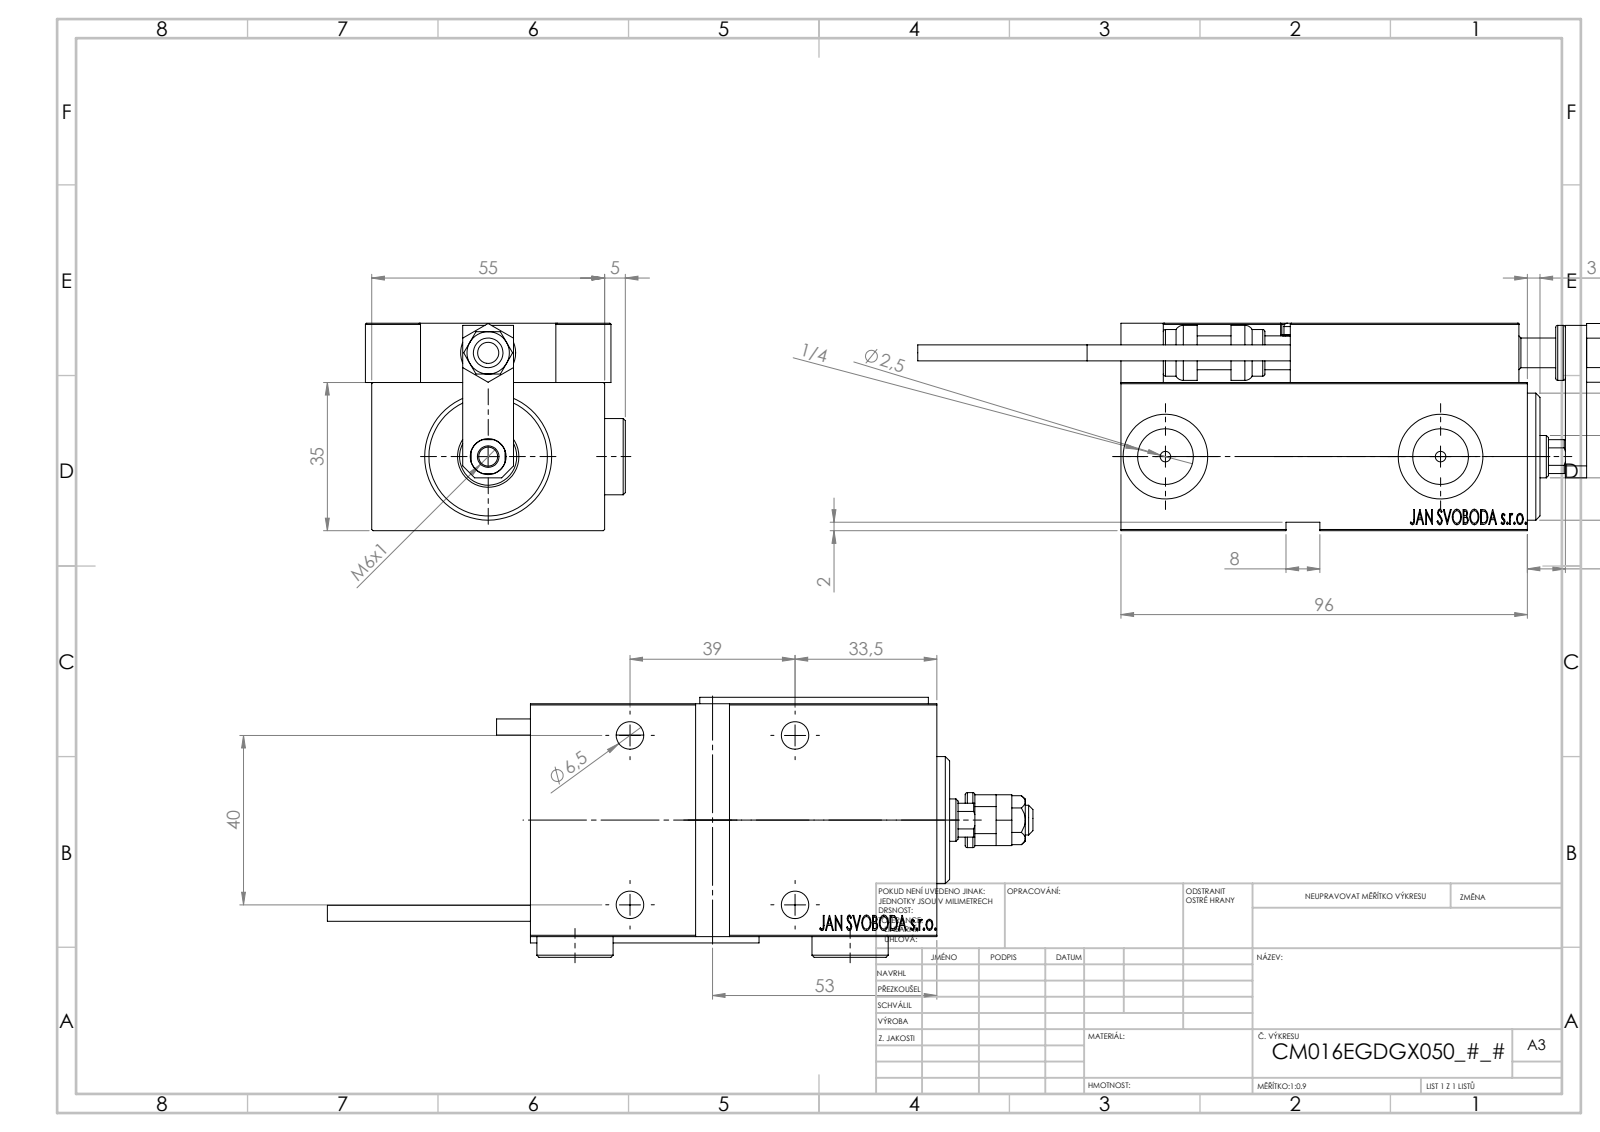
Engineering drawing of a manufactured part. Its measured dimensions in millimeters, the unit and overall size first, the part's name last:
Units: millimetres
Overall size (bounding box): 166.7 × 61.4 × 49
Round holes (diameter × count): ⌀8 ×5, ⌀3.2 ×4, ⌀4 ×4, ⌀6.5 ×4, ⌀10.5 ×4, ⌀2.5 ×2, ⌀5 ×2, ⌀13.16 ×2, ⌀20 ×2, ⌀4.5 ×1, ⌀7 ×1, ⌀8.5 ×1
Round bosses / shafts (diameter × count): ⌀18 ×3, ⌀5 ×2, ⌀3.8 ×2, ⌀30 ×1, ⌀13 ×1, ⌀11 ×1
Partial cylindrical surfaces — rounded edges, fillets, slot ends (radius × count): R0.3 ×30, R3 ×2, R4.5 ×1
Main face-to-face distances: 35, 14, 55, 5, 49, 10, 1.5, 3, 7, 45
Hole centre spacings: 11.37, 20, 21.03, 28.32, 29.59, 29.69, 35.25, 36.06
Volume: 213 227 mm³ · Surface area: 63 202 mm²
Bodies: 26 solids, 1350 faces (605 planar, 200 cylindrical, 545 other)
Part name (STEP PRODUCT): SWITCH DIM B,W; Block; ALLEN BOLT D8; NUT_D12 (+7 more)
STEP written by: SolidWorks 2019 (CONFIG_CONTROL_DESIGN)
